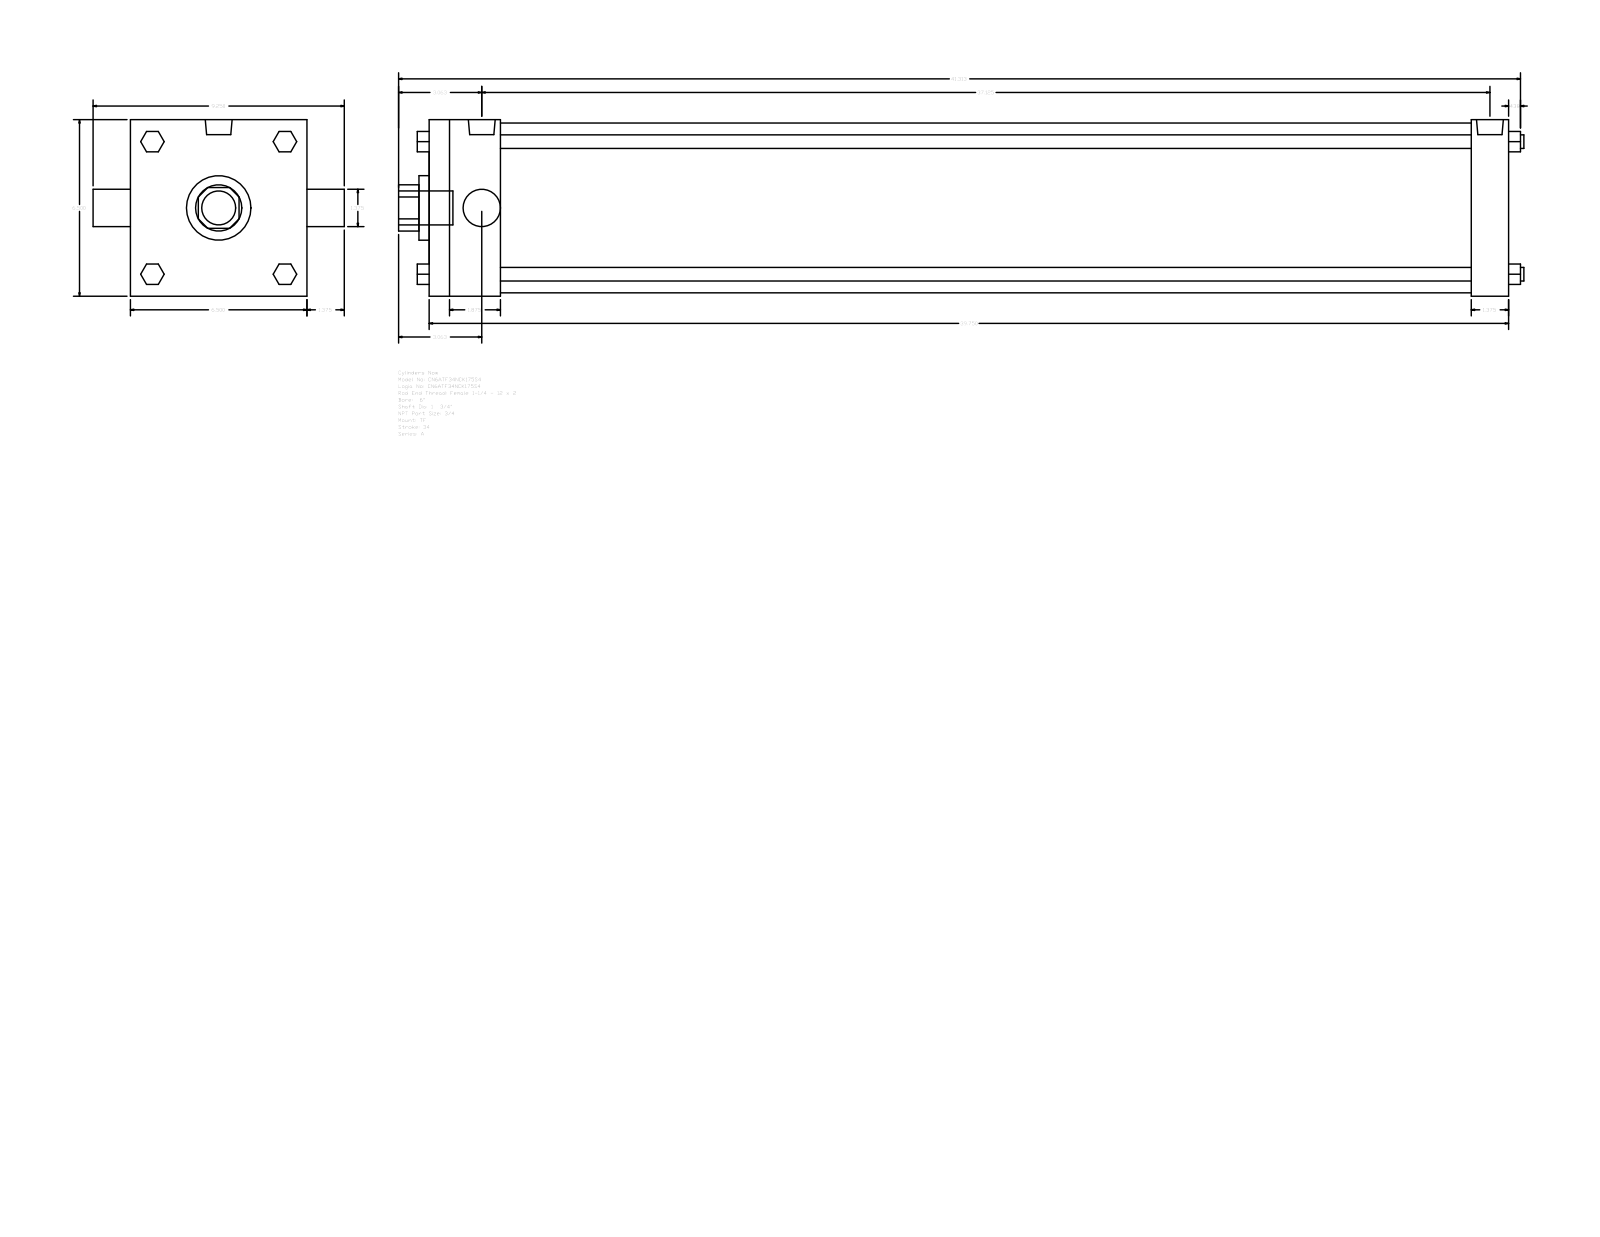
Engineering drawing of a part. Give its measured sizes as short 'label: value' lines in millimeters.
name: A_TF__0600_1.75
written by: GSSL Pune (CONFIG_CONTROL_DESIGN)
unit: mm
bodies: 0 solids, 120 faces (92 planar, 28 cylindrical, 0 other)
size: 1052.51 × 234.95 × 165.1
holes: 1× ⌀34.92, 1× ⌀44.45, 1× ⌀60.33, 1× ⌀158.75
bosses: 4× ⌀12.7, 3× ⌀15.08, 2× ⌀25.12, 1× ⌀31.75
rounds: 1× R21.63
face distances: 165.1, 1009.65, 34.92, 66.68, 942.97, 974.73, 908.05, 19.05, 61.97, 107.34
